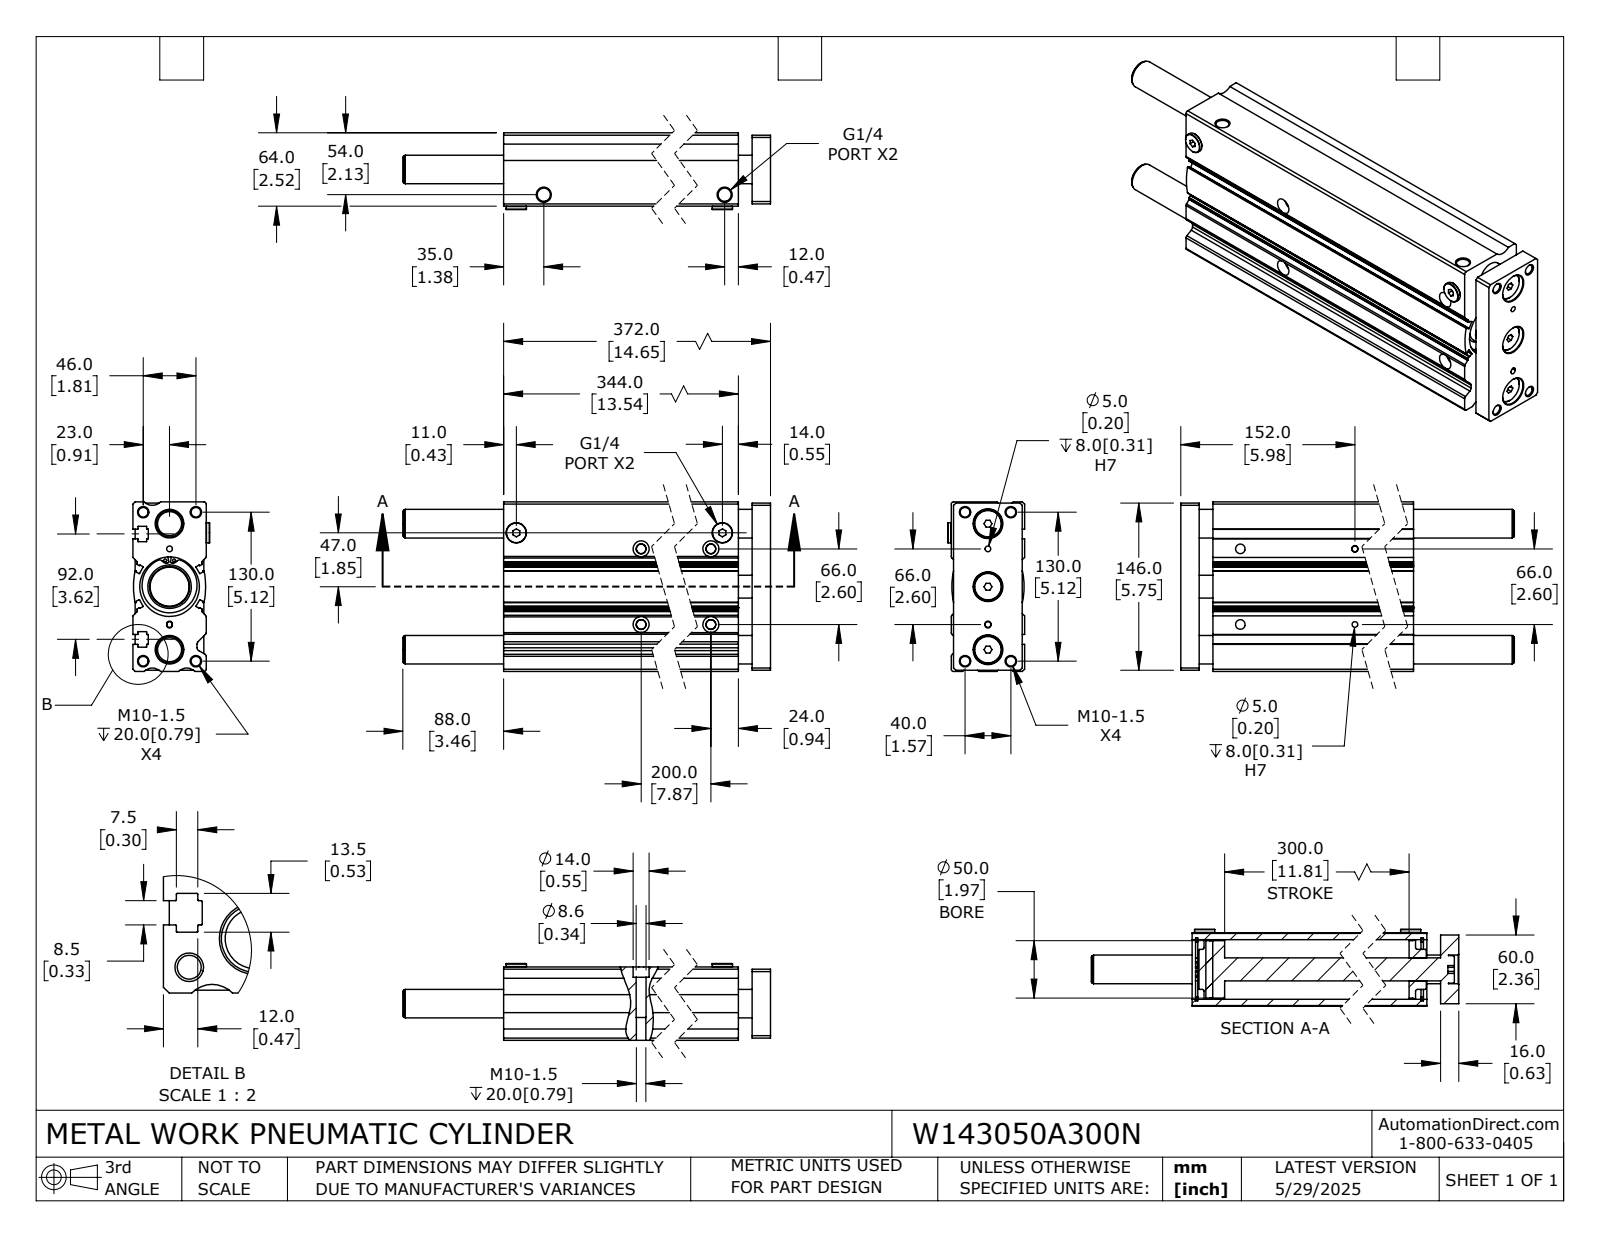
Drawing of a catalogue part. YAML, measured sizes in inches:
part_name: "W143050A300N; W143050A300N_BODY; W143050A300N_ROD"
step_written_by: "SolidWorks 2024 (CONFIG_CONTROL_DESIGN)"
units: inches
bodies: {solids: 6, faces: 466, planar: 186, cylindrical: 224, other: 56}
overall_size: [18.11, 5.827, 2.638]
volume: 160.3
surface_area: 722.3
round_holes:
  - {diameter: 0.33, count: 12}
  - {diameter: 0.098, count: 4}
  - {diameter: 0.197, count: 4}
  - {diameter: 0.339, count: 4}
  - {diameter: 0.551, count: 4}
  - {diameter: 0.984, count: 3}
  - {diameter: 0.451, count: 2}
  - {diameter: 1.89, count: 2}
  - {diameter: 0.787, count: 1}
round_bosses_or_shafts:
  - {diameter: 0.945, count: 3}
  - {diameter: 0.697, count: 2}
  - {diameter: 2.165, count: 1}
  - {diameter: 2.047, count: 1}
  - {diameter: 1.969, count: 1}
  - {diameter: 1.378, count: 1}
partial_cylinders:
  - {radius: 0.012, count: 44}
  - {radius: 0.02, count: 12}
  - {radius: 0.118, count: 10}
  - {radius: 0.079, count: 6}
  - {radius: 2.677, count: 6}
  - {radius: 0.039, count: 4}
  - {radius: 0.098, count: 4}
  - {radius: 0.394, count: 3}
face_to_face_distances: [2.52, 0.472, 5.827, 0.531, 0.098, 3.622, 0.433, 13.543, 0.63, 14.016]
hole_center_spacings: [0.118, 0.424, 0.869, 0.88, 0.916, 0.963, 0.987, 1.271]
